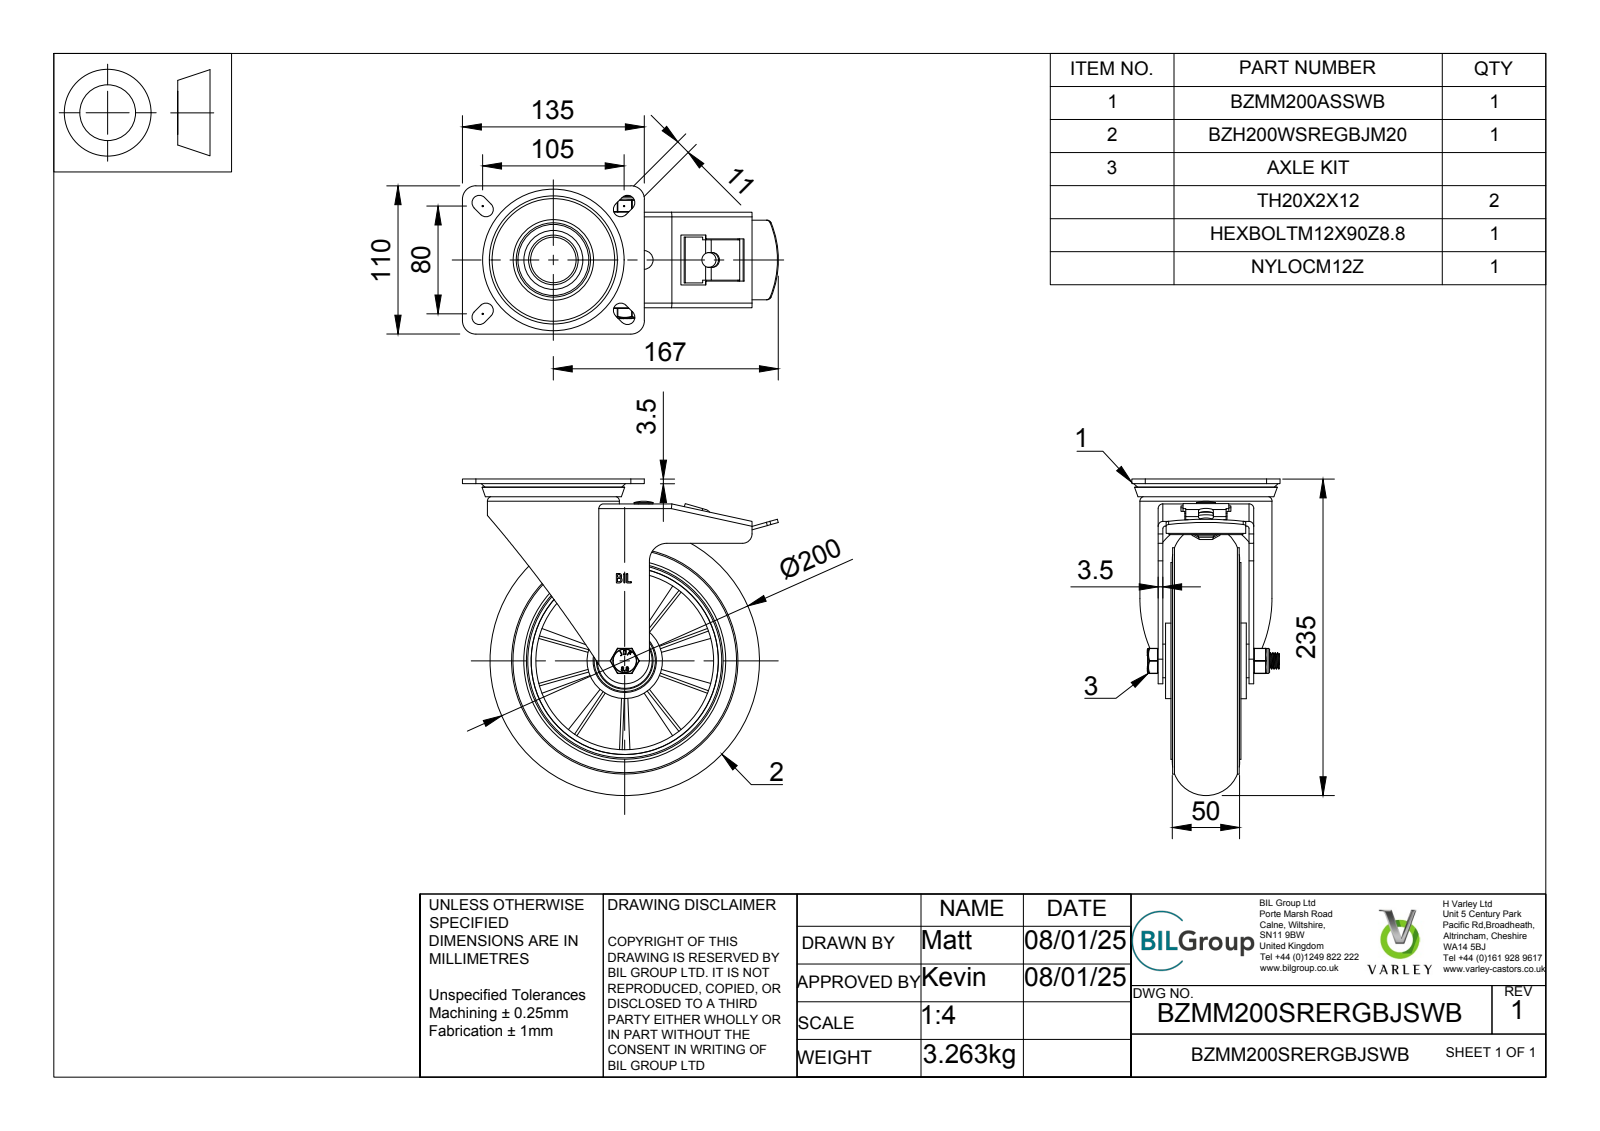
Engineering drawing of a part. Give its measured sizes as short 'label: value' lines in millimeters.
name: BZMM200SRERGBJSWB v3; BZMM200ASSWB - 64 v1; ZINC PLATED, PRESSED STEEL TOP PLATE; ZINC PLATED, PRESSED STEEL TOP PLATE Geometry (+7 more)
written by: Autodesk Translation Framework v13.20.0.188 (AP242_MANAGED_MODEL_BASED_3D_ENGINEERING_MIM_LF)
unit: mm
bodies: 82 solids, 1341 faces (573 planar, 256 cylindrical, 512 other)
size: 235 × 234.5 × 110
volume: 1 106 000 mm³; area: 381 344 mm²
holes: 1× ⌀8, 1× ⌀11, 1× ⌀12, 1× ⌀12.2, 1× ⌀14, 1× ⌀20, 1× ⌀28.5, 1× ⌀30.8, 1× ⌀33.75, 1× ⌀40.3, 1× ⌀40.5, 1× ⌀42
bosses: 1× ⌀168, 1× ⌀146, 1× ⌀98, 1× ⌀78, 1× ⌀56.2, 1× ⌀56, 1× ⌀50, 1× ⌀40.8
rounds: 19× R0.5, 10× R5.5, 7× R1.75, 6× R0.25, 6× R2.5, 4× R0.47, 4× R0.9, 4× R3.5
face distances: 3.5, 2, 9, 5.5, 13, 67.5, 47.75, 14.25, 4, 9.5
hole spacings: 67
